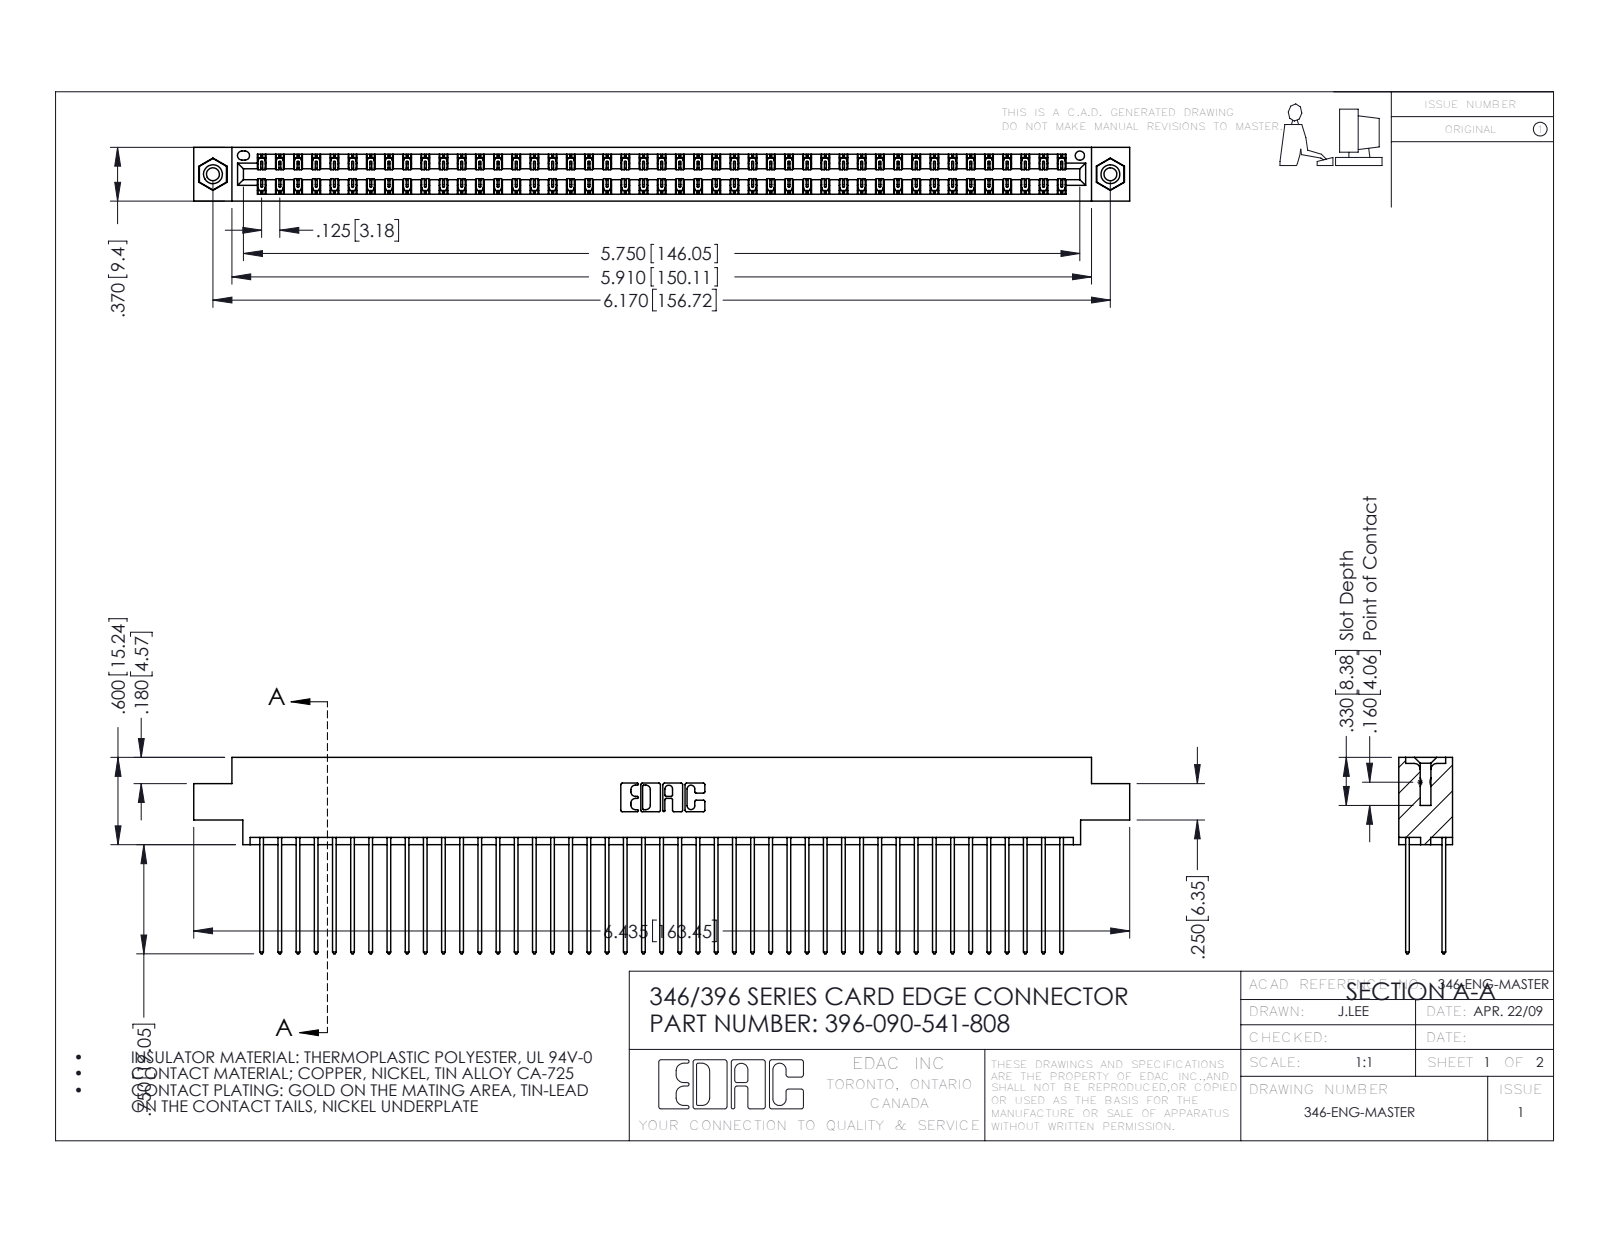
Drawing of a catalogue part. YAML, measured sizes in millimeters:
part_name: "346 Part_0.170 Offset - 0.156 Dia-TI; 345-292-001_345-293-141; 396-090-541-808; 345-250-001_345-250-003-102"
step_written_by: "SolidWorks 2016 (CONFIG_CONTROL_DESIGN)"
units: millimeters
bodies: {solids: 93, faces: 4866, planar: 3262, cylindrical: 1588, other: 16}
overall_size: [163.4, 34.3, 9.4]
volume: 16300
surface_area: 25150
round_holes:
  - {diameter: 2.3, count: 2}
  - {diameter: 3.2, count: 2}
  - {diameter: 4, count: 2}
  - {diameter: 1.6, count: 1}
round_bosses_or_shafts:
  - {diameter: 3.9, count: 2}
partial_cylinders:
  - {radius: 0.2, count: 135}
  - {radius: 0.3, count: 90}
  - {radius: 0.3, count: 22}
  - {radius: 0.2, count: 6}
  - {radius: 0.8, count: 6}
  - {radius: 0.7, count: 3}
  - {radius: 0.4, count: 2}
  - {radius: 0.6, count: 2}
face_to_face_distances: [1.2, 8.2, 6.4, 1.8, 7.6, 0.6, 9.4, 7, 5.7, 5.6]
hole_center_spacings: [6.2, 151.4, 156.7]
